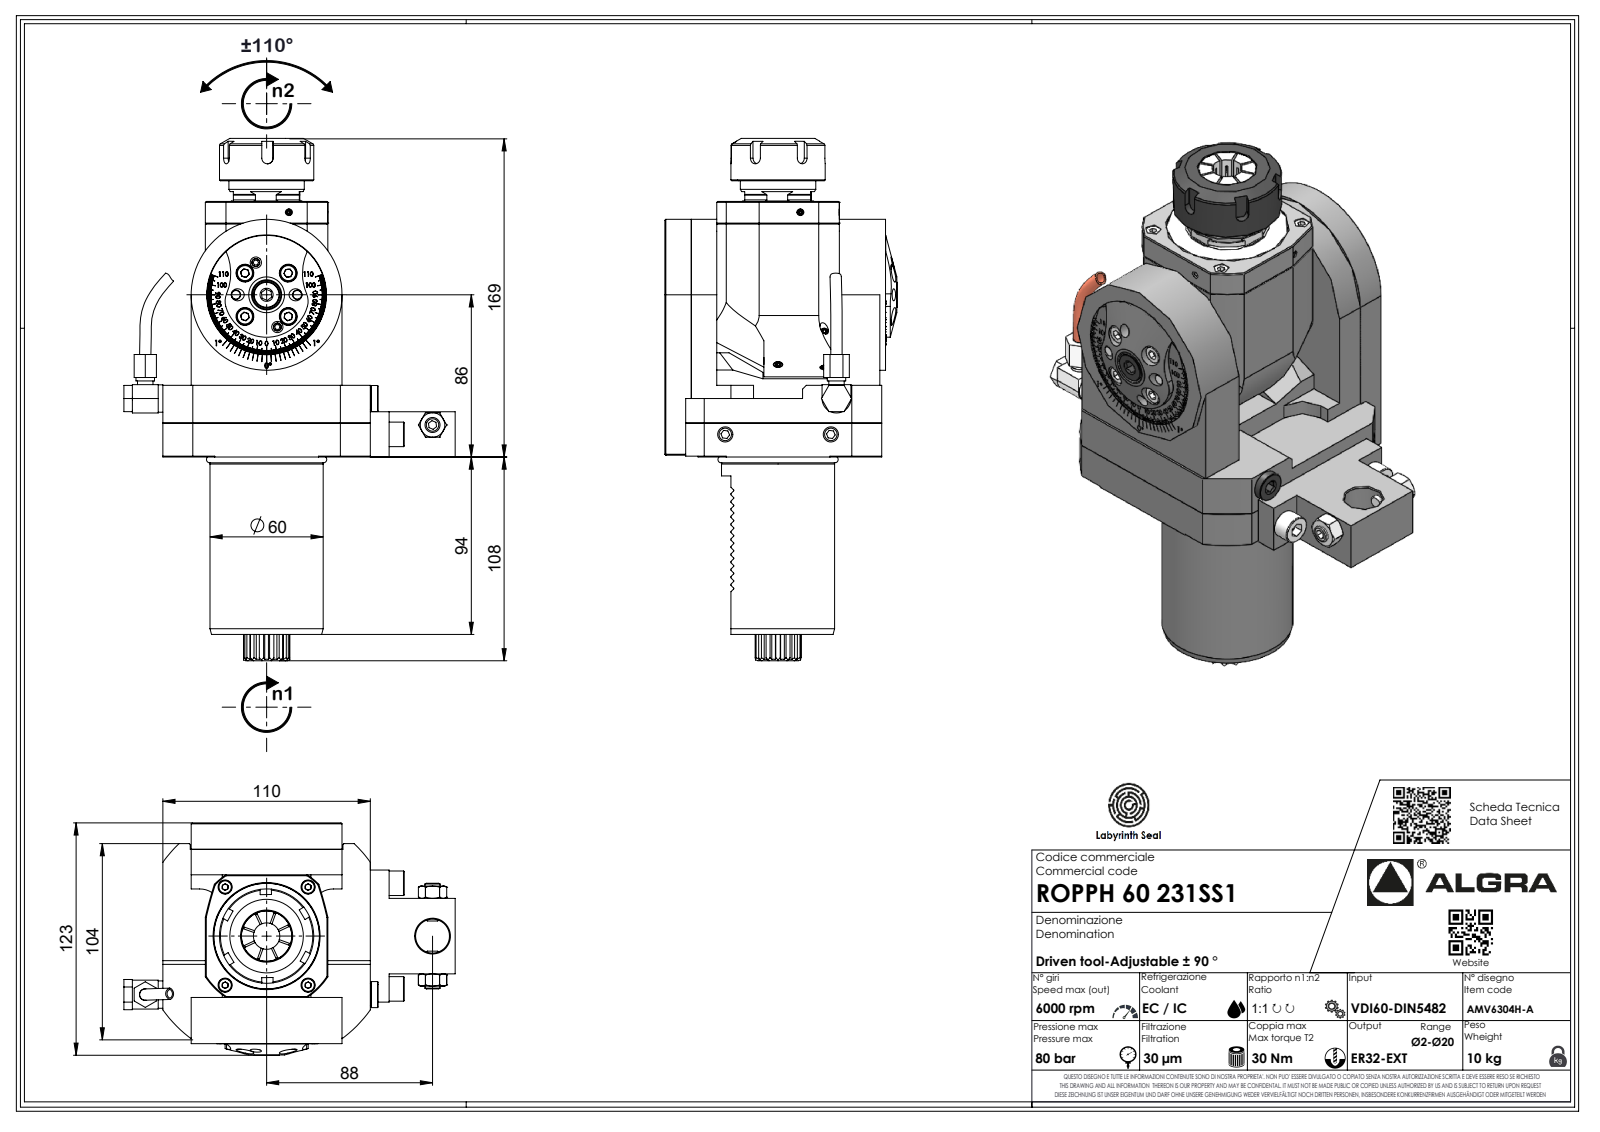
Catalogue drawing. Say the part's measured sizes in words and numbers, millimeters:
The part is named "ROPPH60231SS1". Its 3-D file was written by "SolidWorks 2023 (AUTOMOTIVE_DESIGN)". It is 1 solid with 708 faces: 427 planar, 132 cylindrical and 149 other. Overall it measures 276.91 by 175.7 by 123 millimeters. Its volume is 1 485 000 cubic millimeters and its surface area 127 513 square millimeters. Round holes: 1 of diameter 2.1, 1 of diameter 44.2, 1 of diameter 48.2, 1 of diameter 52.2, 1 of diameter 56.2. Round bosses or shafts: 1 of diameter 80, 1 of diameter 60, 1 of diameter 58.7, 1 of diameter 56, 1 of diameter 52, 1 of diameter 50, 1 of diameter 44, 1 of diameter 40. Partial cylindrical surfaces (rounded edges, fillets, slot ends): 14 of radius 0.3, 7 of radius 0.33, 7 of radius 0.52, 7 of radius 3.7, 5 of radius 3, 3 of radius 0.2, 2 of radius 10, 2 of radius 12. The main face-to-face distances are 22.5, 87.5, 65, 80, 7.5, 7, 95, 135.5, 27.5, 94.
